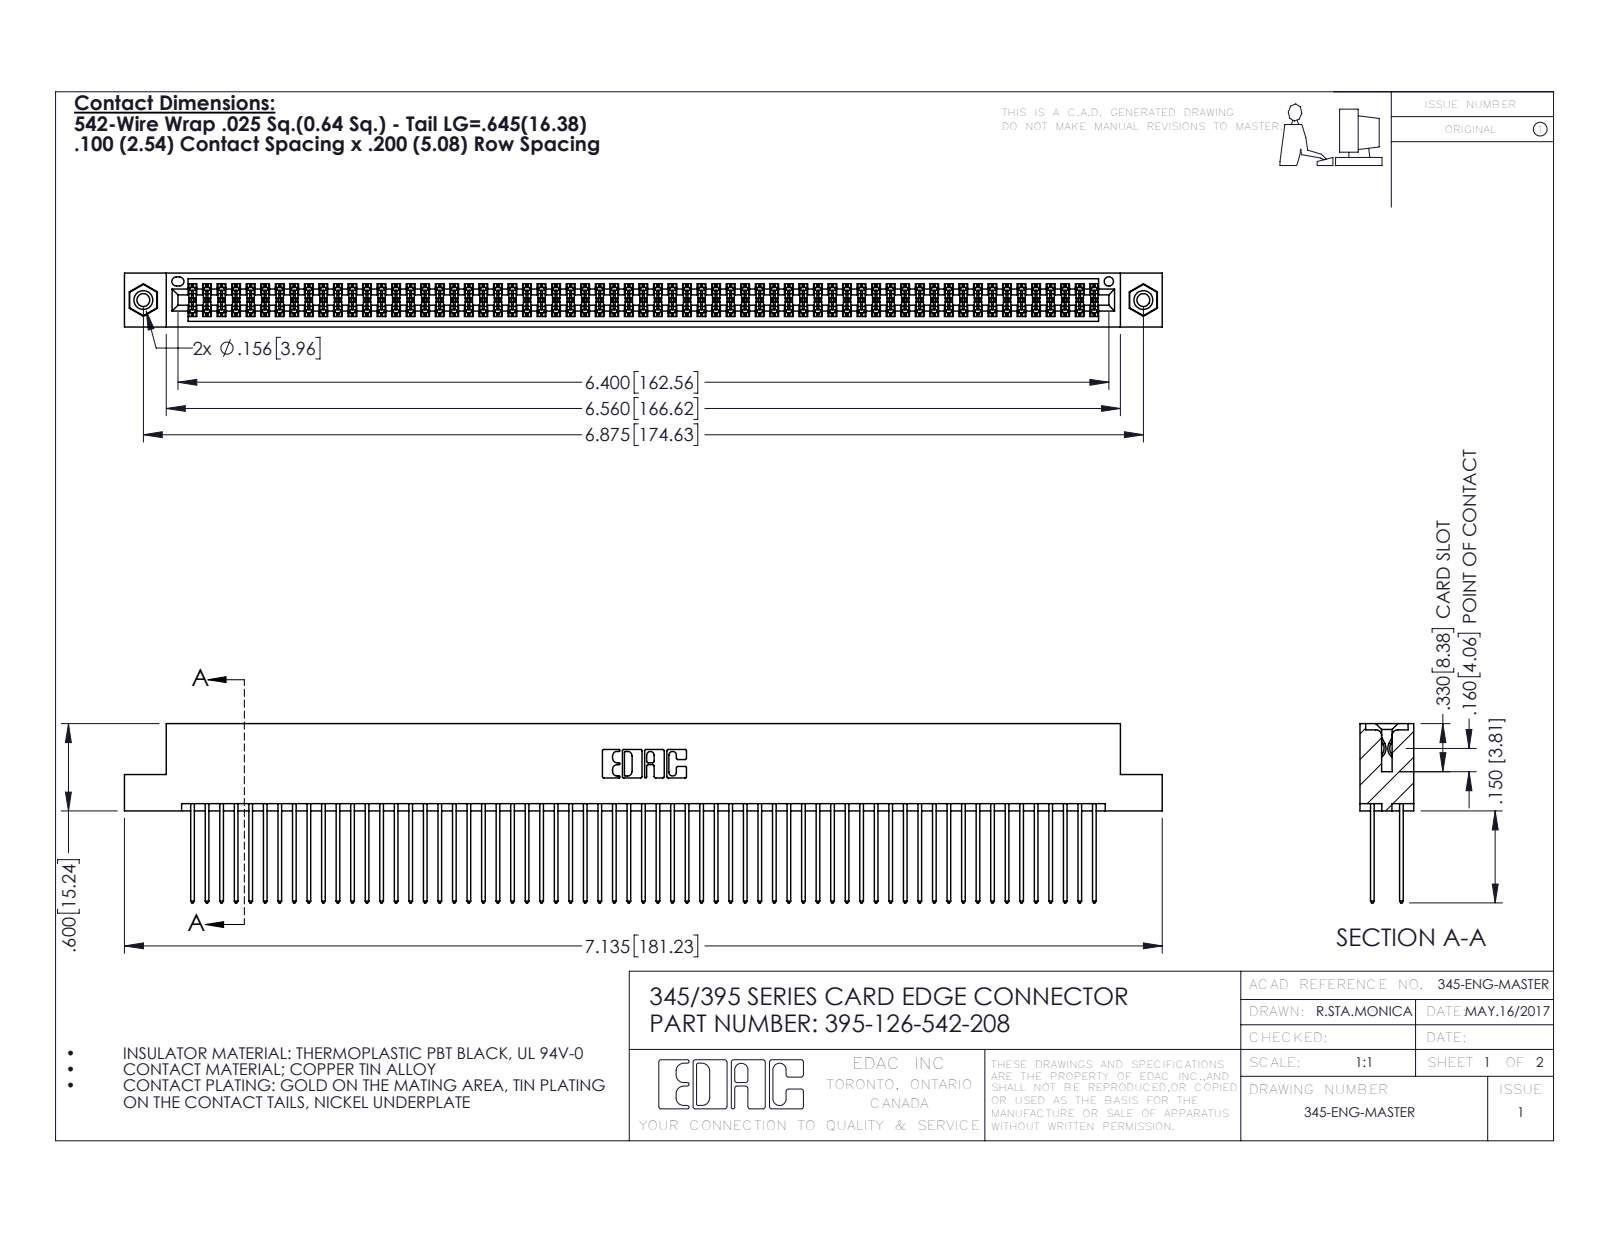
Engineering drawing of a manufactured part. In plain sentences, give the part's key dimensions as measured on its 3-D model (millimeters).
The part is named "395-126-542-208; 345 Part_Flush Mounting Lugs - 0.156 Dia-TI; 345-292-001_345-293-142; 345-250-001_345-250-003-102". Its 3-D file was written by "SolidWorks 2016 (CONFIG_CONTROL_DESIGN)". It is 129 solids with 6486 faces: 4270 planar, 2200 cylindrical and 16 other. Overall it measures 181.2 by 31.3 by 9.4 millimeters. Its volume is 18 390 cubic millimeters and its surface area 30 340 square millimeters. Round holes: 2 of diameter 2.3, 2 of diameter 3.2, 2 of diameter 4, 1 of diameter 1.6. Round bosses or shafts: 2 of diameter 3.9. Partial cylindrical surfaces (rounded edges, fillets, slot ends): 189 of radius 0.2, 126 of radius 0.3, 22 of radius 0.3, 6 of radius 0.2, 6 of radius 0.8, 3 of radius 0.7, 2 of radius 0.4, 2 of radius 0.5. The main face-to-face distances are 1.8, 7.6, 5.1, 2.5, 6.9, 0.6, 5.7, 9.4, 4.4, 3.8. The hole center spacings are 6.9, 168.6, 174.6.
